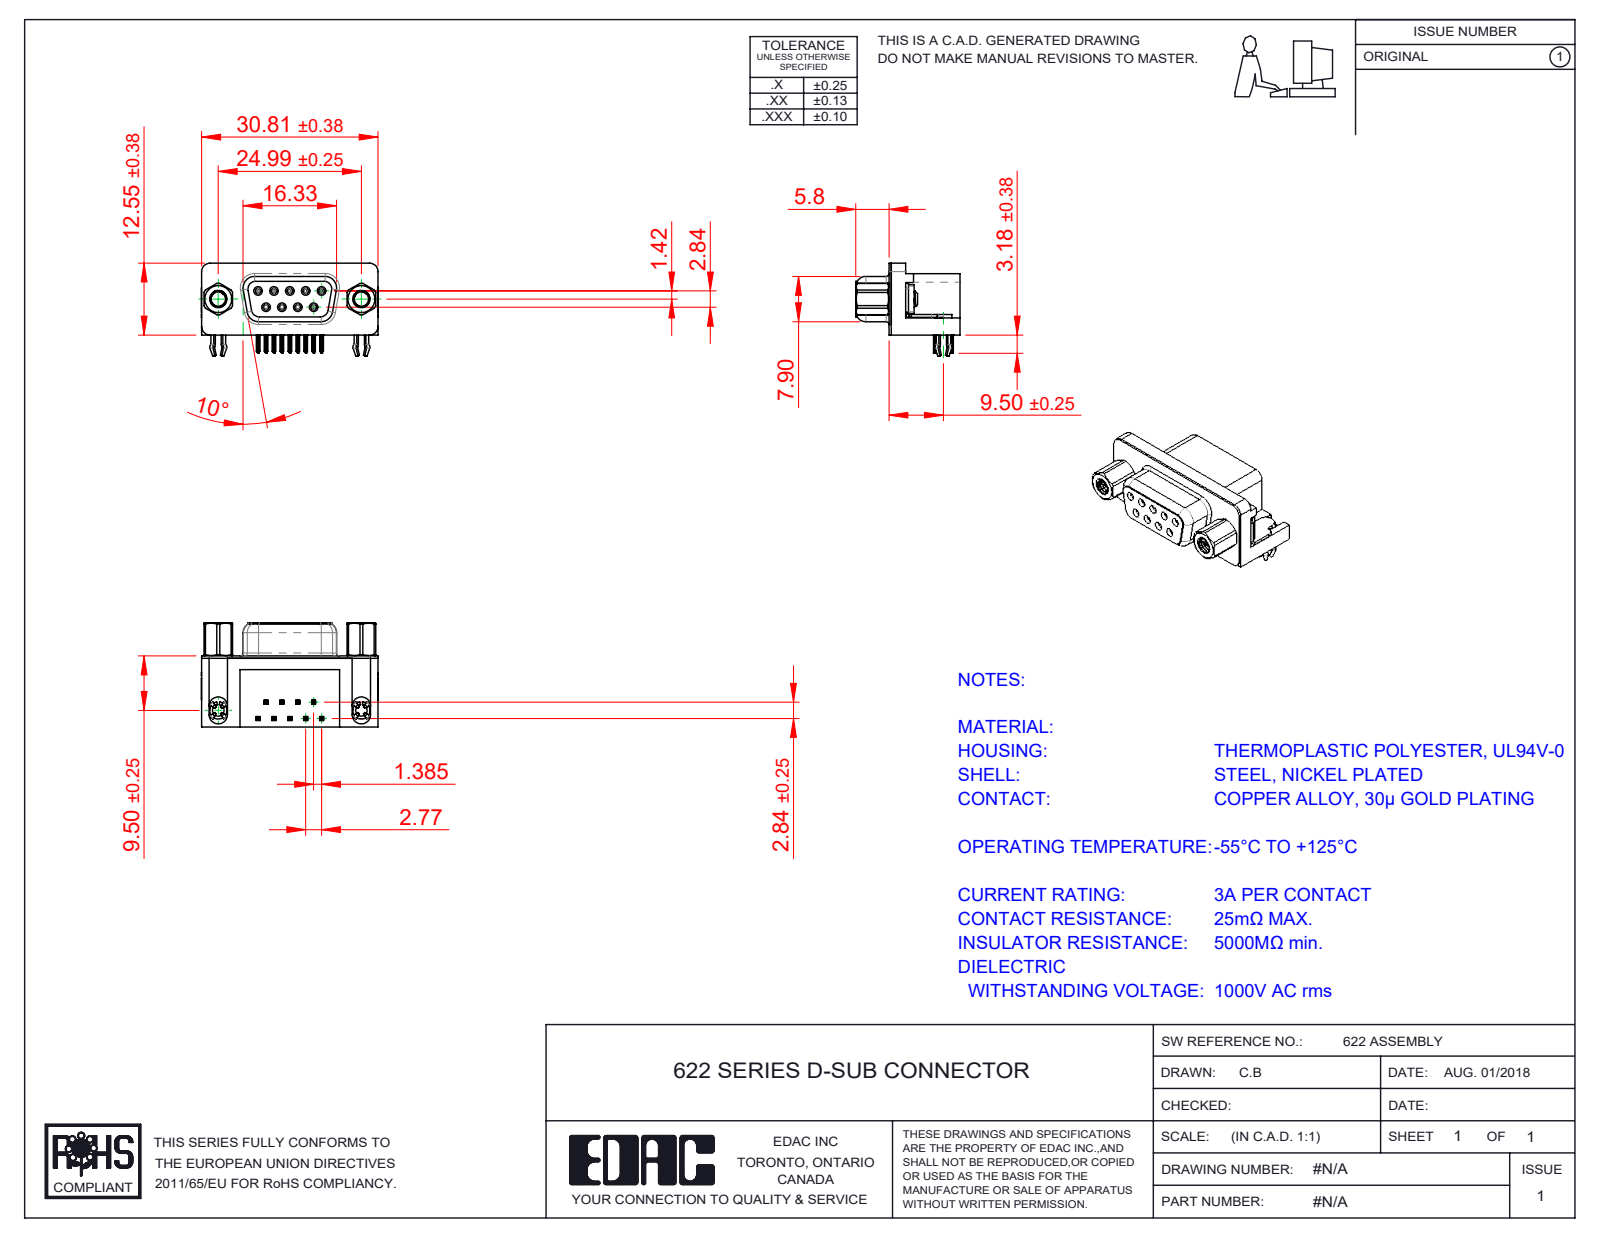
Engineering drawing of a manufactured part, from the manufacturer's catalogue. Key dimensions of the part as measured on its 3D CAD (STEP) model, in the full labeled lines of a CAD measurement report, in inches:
Part name (STEP PRODUCT): 622 4-40 Threaded Board Mount; 622 Housing_9 Socket; 622 Contact Top; 622-009-660-556 (+3 more)
STEP written by: SolidWorks 2016 (CONFIG_CONTROL_DESIGN)
Units: inches
Bodies: 15 solids, 1602 faces (684 planar, 432 cylindrical, 486 other)
Overall size (bounding box): 1.216 × 0.717 × 0.619
Volume: 0.228 in³ · Surface area: 7.992 in²
Round holes (diameter × count): ⌀0.031 ×9, ⌀0.035 ×9, ⌀0.089 ×2, ⌀0.098 ×2, ⌀0.157 ×2, ⌀0.189 ×2, ⌀0.197 ×2
Round bosses / shafts (diameter × count): ⌀0.047 ×9, ⌀0.193 ×2, ⌀0.187 ×2, ⌀0.154 ×2, ⌀0.128 ×2
Partial cylindrical surfaces — rounded edges, fillets, slot ends (radius × count): R0.004 ×72, R0.006 ×36, R0.014 ×18, R0.039 ×18, R0.013 ×9, R0.01 ×8, R0.053 ×8, R0.063 ×8
Main face-to-face distances: 0.016, 0.472, 0.488, 0.014, 0.114, 0.098, 0.244, 0.407, 0.374, 0.228
Hole centre spacings: 0.124, 0.109, 0.218, 0.198, 0.198, 0.327, 0.294, 0.295
